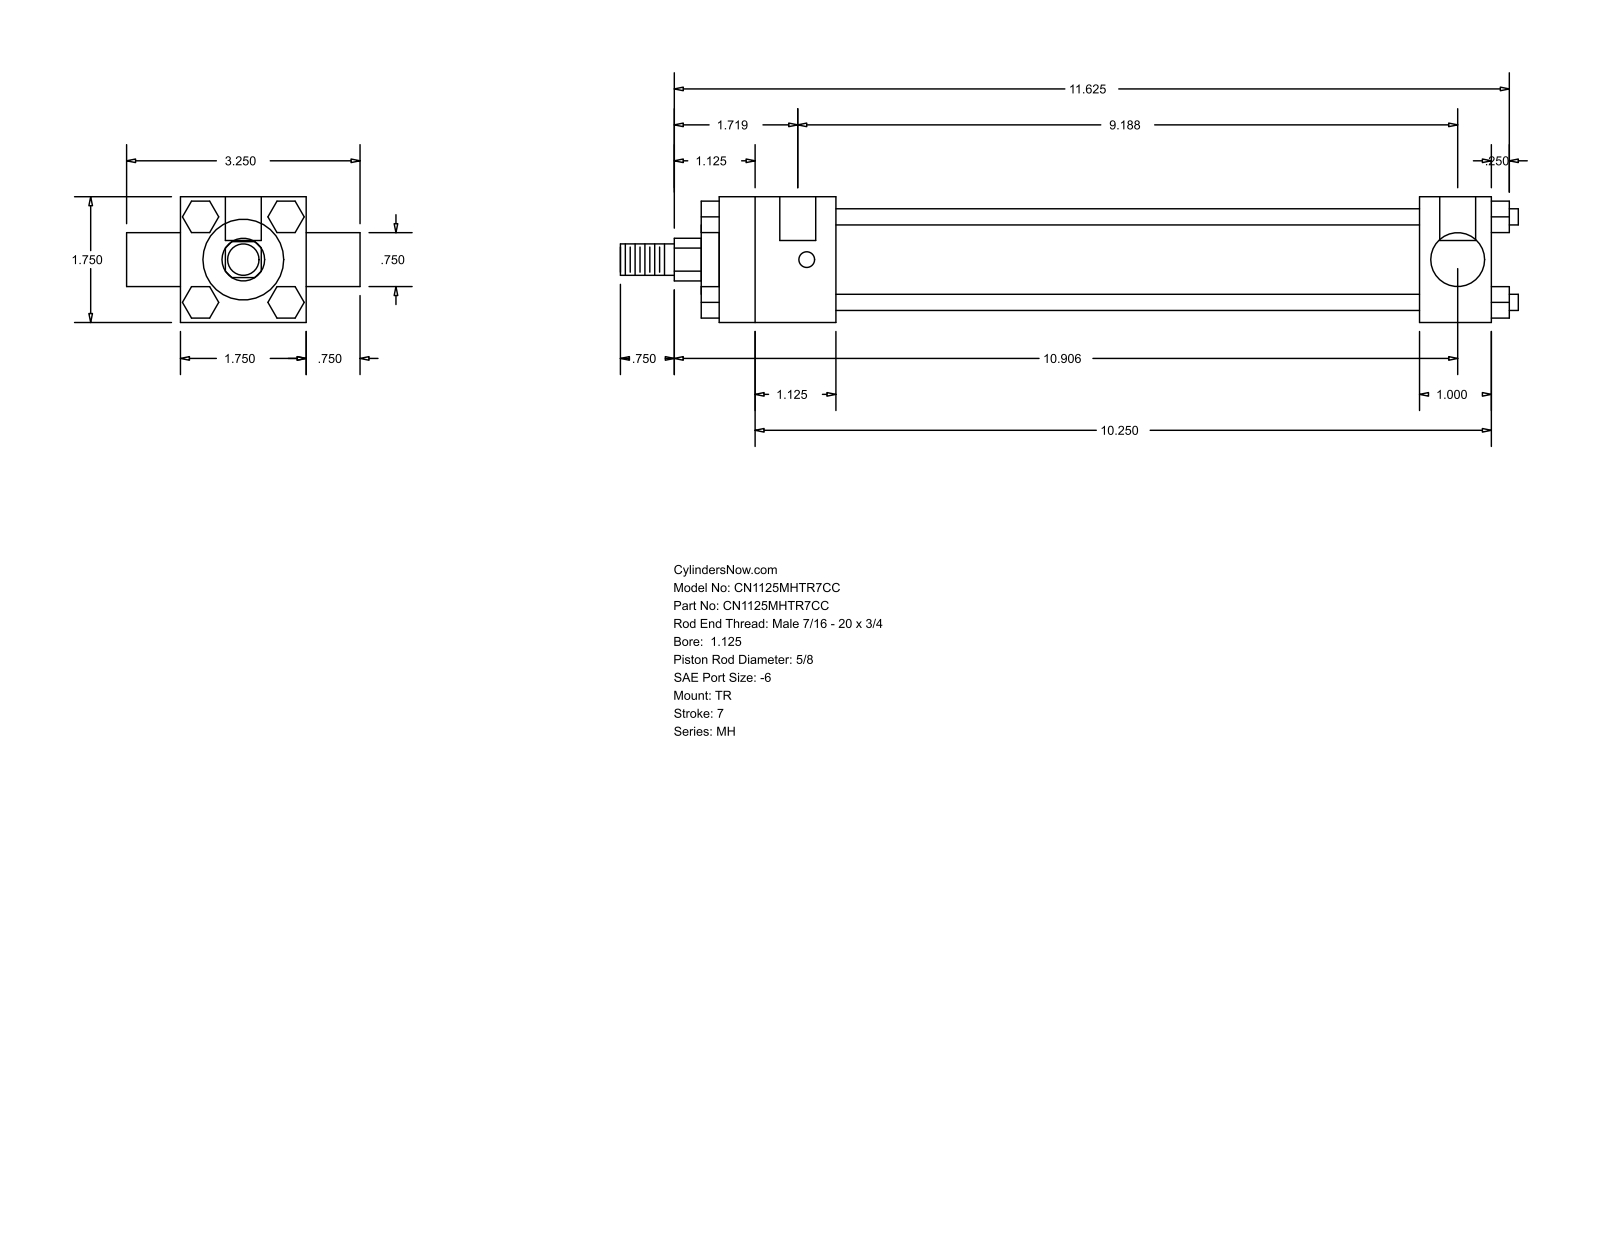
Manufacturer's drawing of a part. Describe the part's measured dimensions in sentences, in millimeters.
The part is named "MH_TR__0112_0.625". Its 3-D file was written by "GSSL Pune (CONFIG_CONTROL_DESIGN)". It is 0 solids with 120 faces: 92 planar, 28 cylindrical and 0 other. Overall it measures 317.5 by 82.55 by 44.45 millimeters. Round holes: 3 of diameter 5.56, 2 of diameter 12.7. Round bosses or shafts: 4 of diameter 5.71, 1 of diameter 34.92, 1 of diameter 28.57, 1 of diameter 19.05, 1 of diameter 15.88, 1 of diameter 11.11. Partial cylindrical surfaces (rounded edges, fillets, slot ends): 1 of radius 7.54. The main face-to-face distances are 44.46, 11.11, 206.37, 231.78, 25.41, 41.27, 247.64, 273.05, 47.62, 6.35. The hole center spacings are 3.17, 230.19, 233.36.
